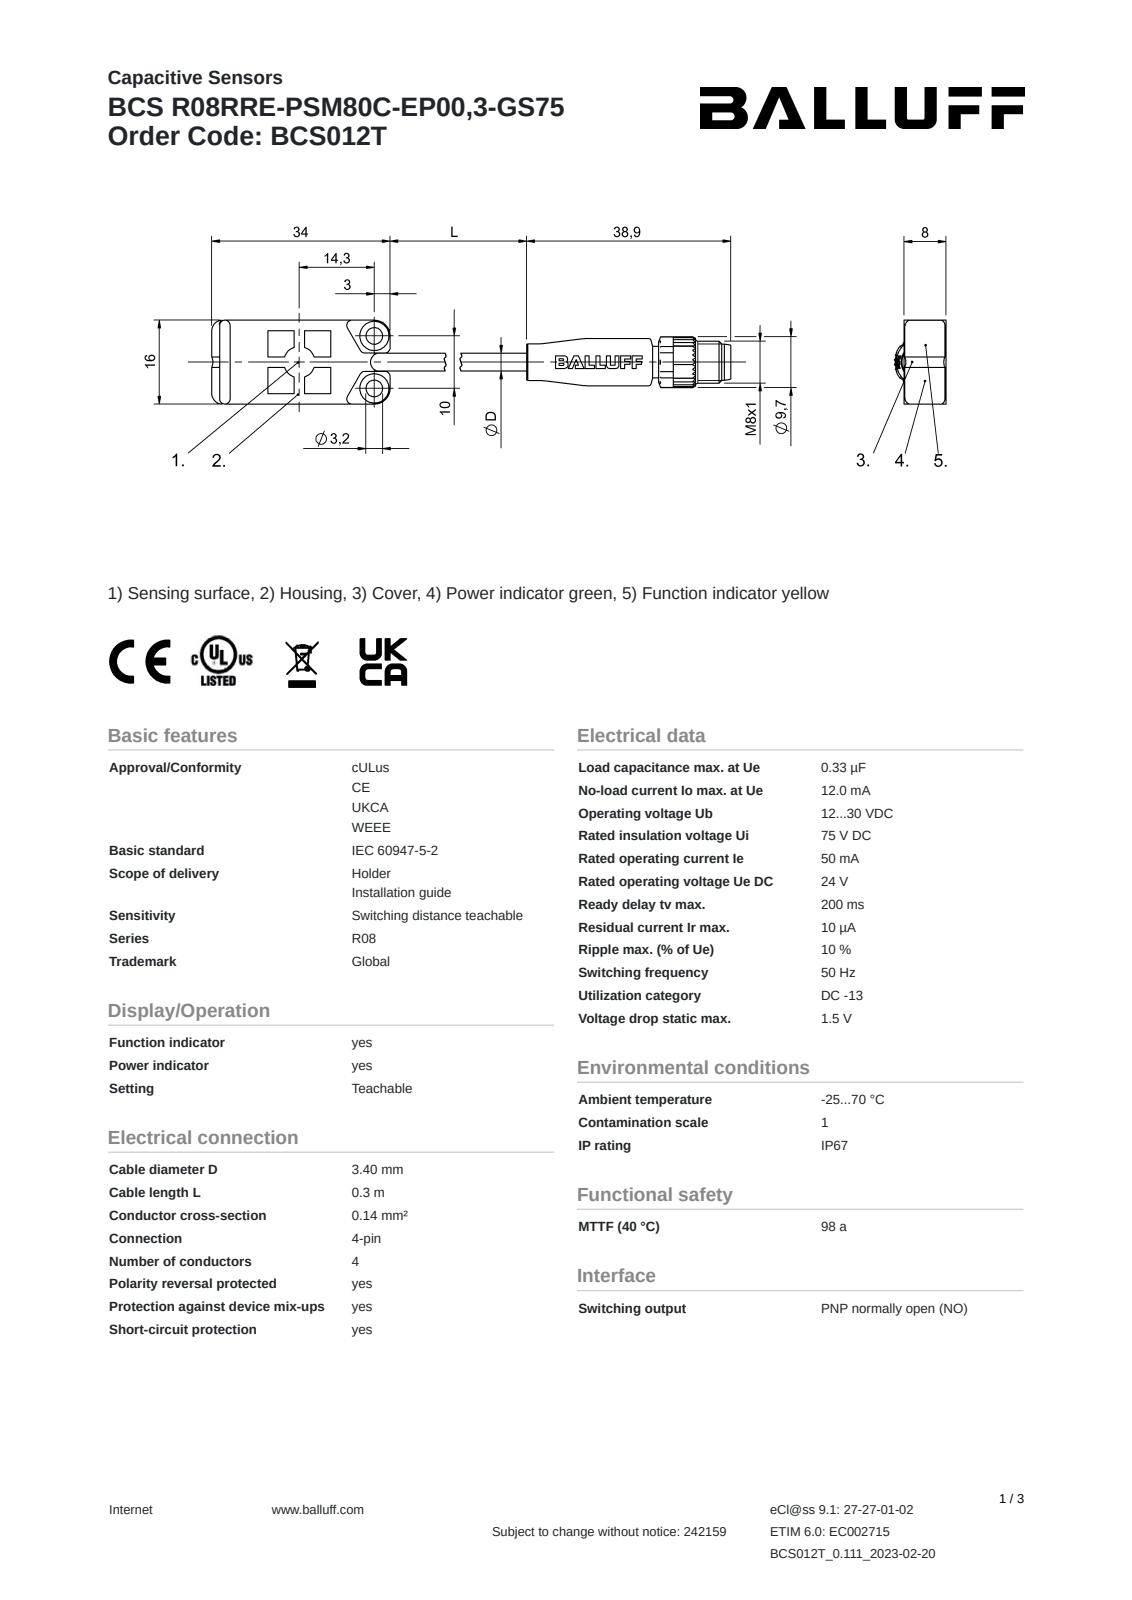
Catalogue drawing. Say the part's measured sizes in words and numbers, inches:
The part is named "BCS012T". Its 3-D file was written by "SolidWorks 2021 (AUTOMOTIVE_DESIGN)". It is 3 solids with 1016 faces: 661 planar, 295 cylindrical and 60 other. Overall it measures 4.661 by 2.953 by 0.387 inches. Its volume is 0.729 cubic inches and its surface area 15.14 square inches. Round holes: 6 of diameter 0.126, 1 of diameter 0.087, 1 of diameter 0.224. Round bosses or shafts: 4 of diameter 0.039, 2 of diameter 0.079, 1 of diameter 0.354, 1 of diameter 0.315, 1 of diameter 0.303, 1 of diameter 0.276, 1 of diameter 0.267, 1 of diameter 0.236. Partial cylindrical surfaces (rounded edges, fillets, slot ends): 54 of radius 0.006, 22 of radius 0.039, 16 of radius 0.031, 14 of radius 0.079, 8 of radius 0.016, 6 of radius 0.008, 4 of radius 0.02, 4 of radius 0.033. The main face-to-face distances are 0.15, 0.039, 0.118, 0.157, 0.307, 0.634, 0.031, 0.268, 0.059, 0.299. The hole center spacings are 0.4, 0.837, 1.163, 1.168, 1.526, 2.053, 0.394, 0.567.
